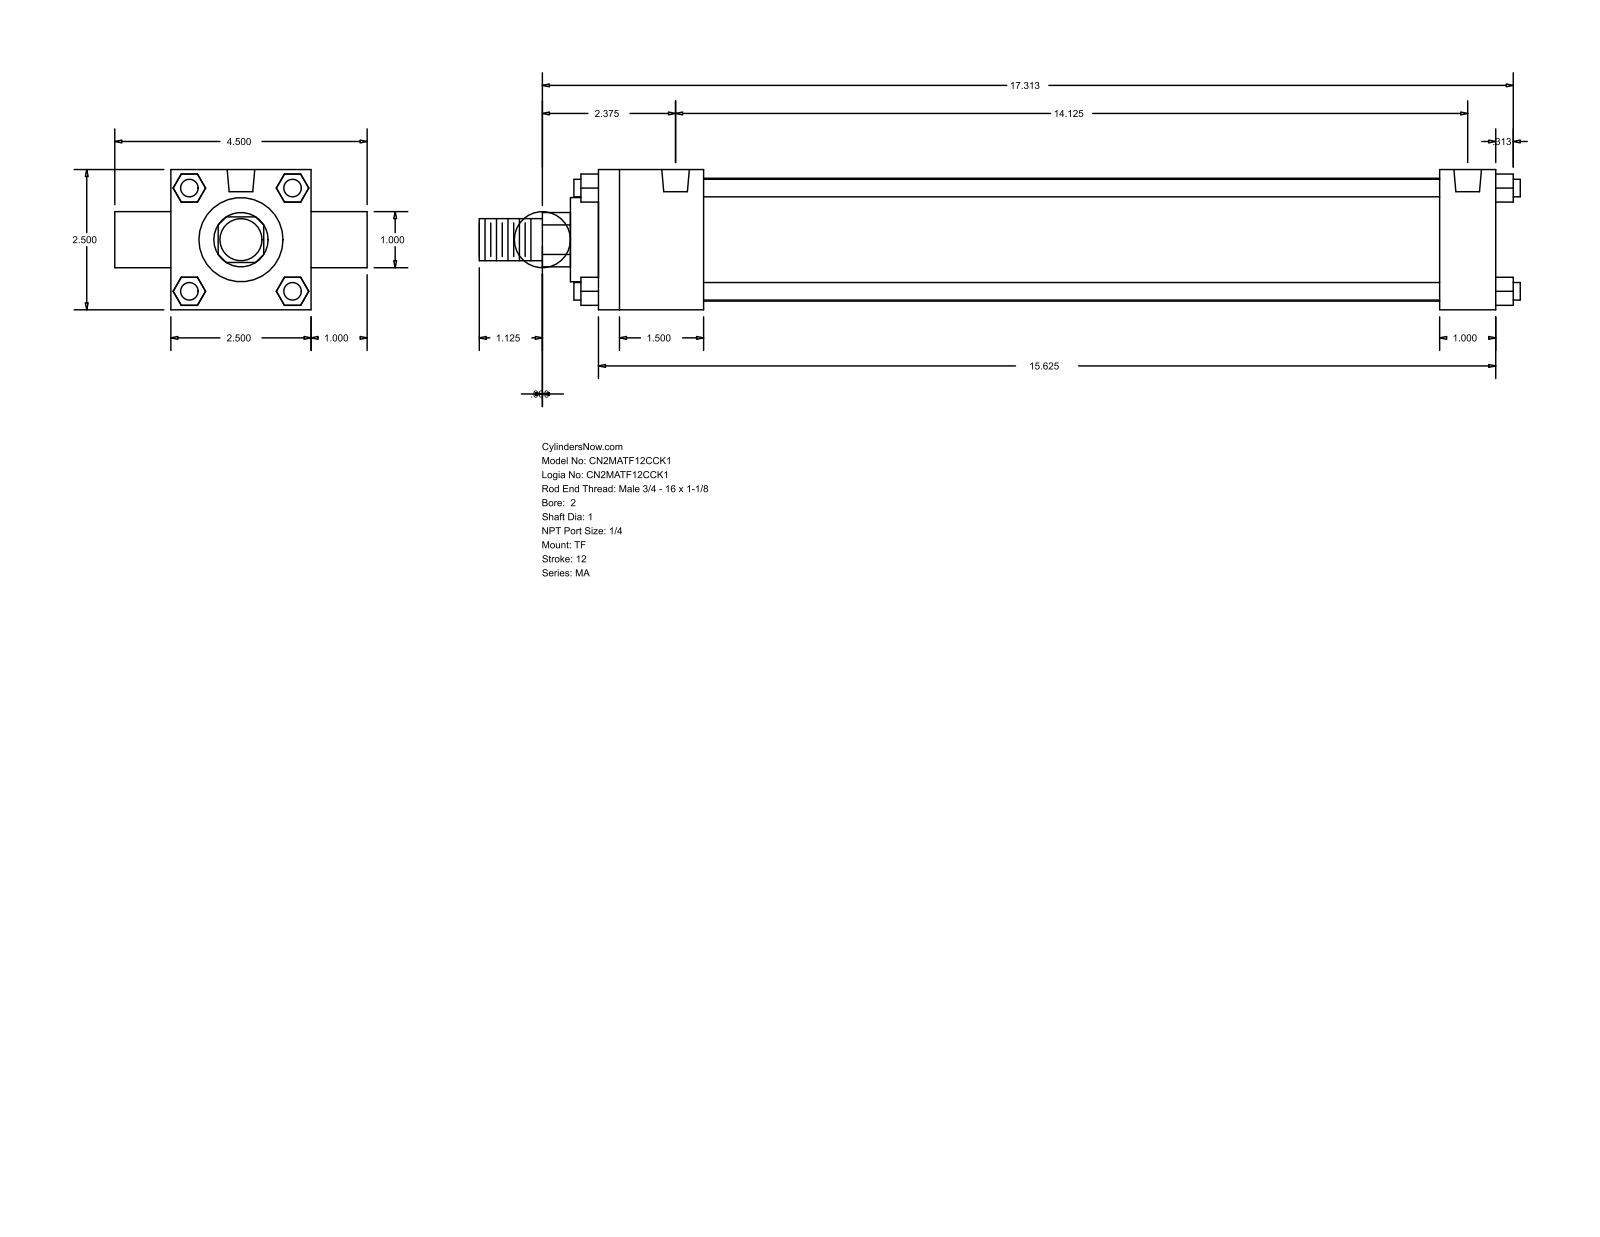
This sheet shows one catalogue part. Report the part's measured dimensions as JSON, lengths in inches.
{"part_name": "MA_TF__0200_1", "step_written_by": "GSSL Pune (CONFIG_CONTROL_DESIGN)", "units": "inches", "bodies": {"solids": 0, "faces": 120, "planar": 92, "cylindrical": 28, "other": 0}, "overall_size": [18.563, 4.5, 2.5], "round_holes": [[0.313, 3], [0.492, 2]], "round_bosses_or_shafts": [[0.313, 4], [1, 2], [2.19, 1], [1.5, 1], [0.75, 1]], "partial_cylinders_radius": [[0.484, 1]], "face_to_face_distances": [2.5, 1, 16, 0.5, 1.875, 15, 13.125, 14.125, 3.5, 1.593], "hole_center_spacings": [14.125]}
